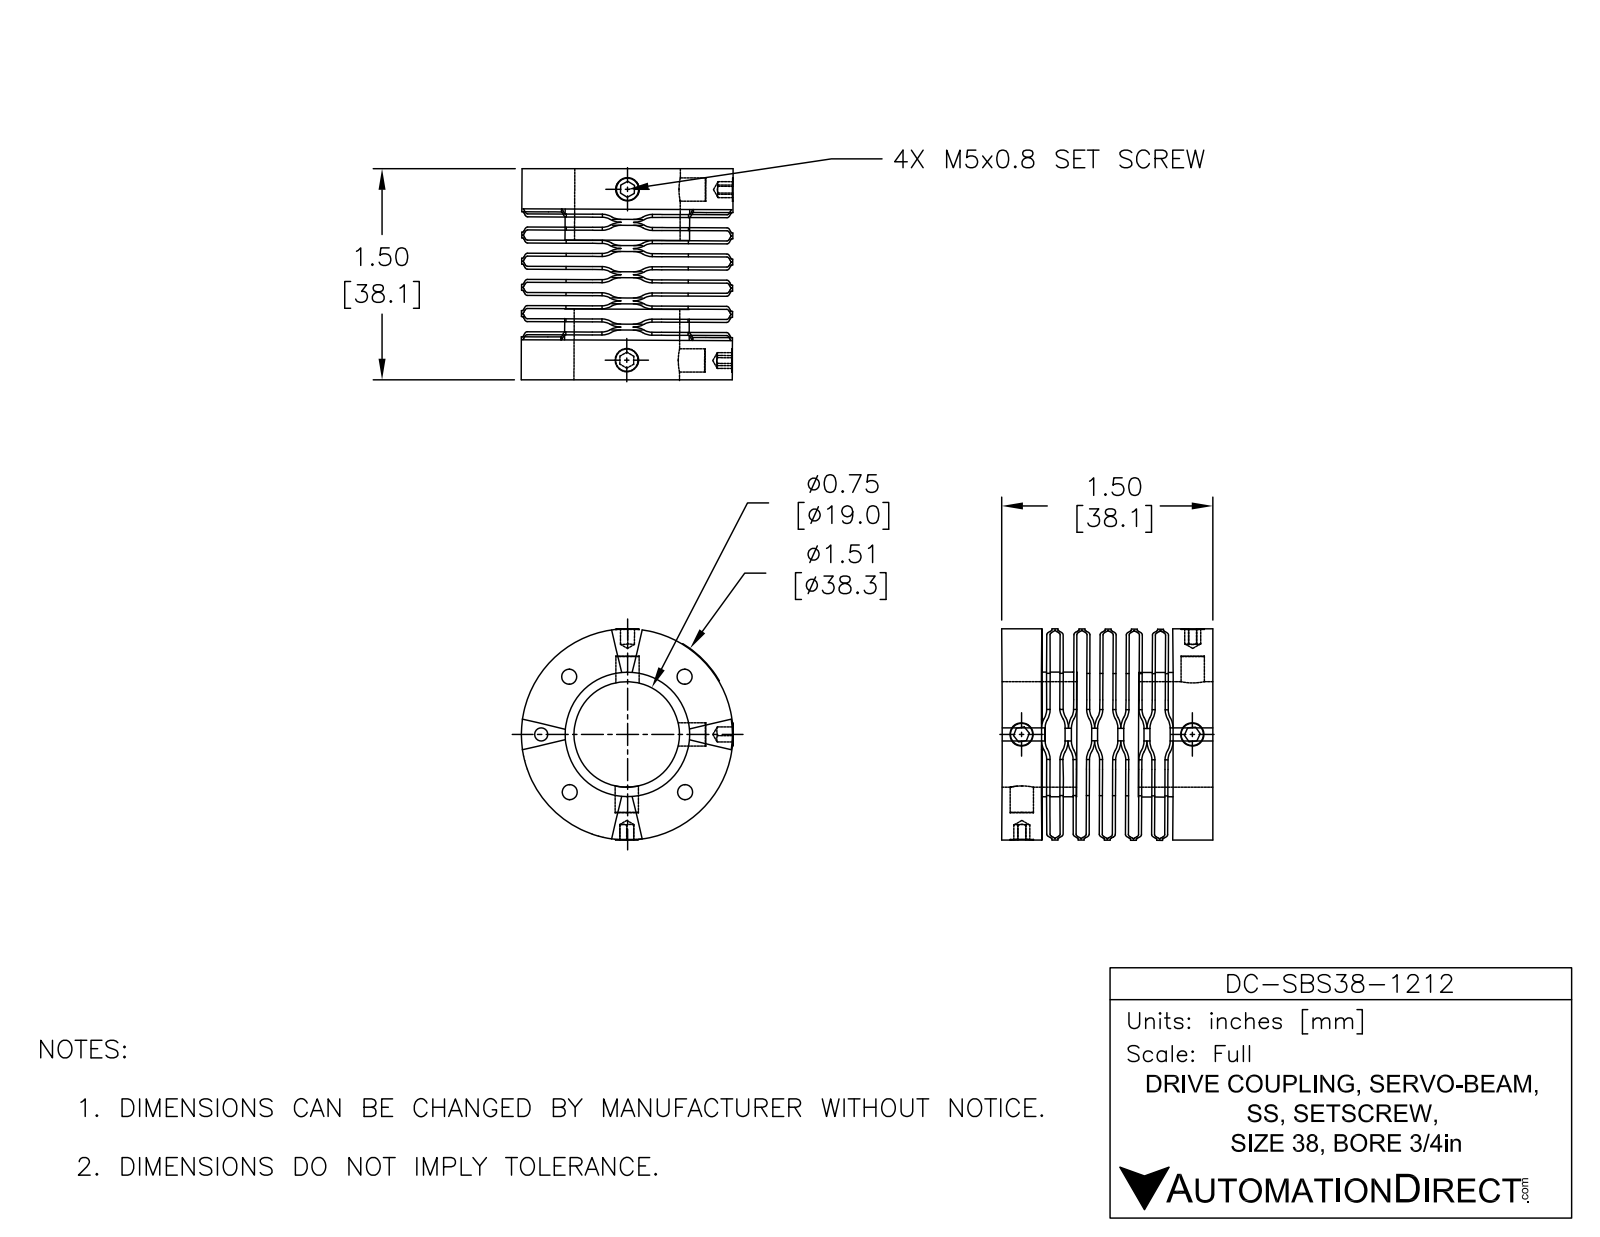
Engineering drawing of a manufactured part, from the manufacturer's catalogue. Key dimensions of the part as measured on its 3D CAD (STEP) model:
Part name (STEP PRODUCT): DC-SBS38-1212
STEP written by: SolidWorks 2015 (AUTOMOTIVE_DESIGN)
Units: millimetres
Bodies: 17 solids, 789 faces (369 planar, 364 cylindrical, 56 other)
Overall size (bounding box): 38.5 × 38.34 × 38.08
Volume: 17 807 mm³ · Surface area: 23 803 mm²
Round holes (diameter × count): ⌀4.2 ×4, ⌀19.05 ×1, ⌀23.76 ×1
Round bosses / shafts (diameter × count): ⌀4.2 ×3, ⌀4.2 ×1
Partial cylindrical surfaces — rounded edges, fillets, slot ends (radius × count): R1.5 ×320
Main face-to-face distances: 4.72, 9.44, 14.16, 0.53, 2.37, 1.84, 5.25, 7.09, 6.56, 2.88
Hole centre spacings: 30.48
